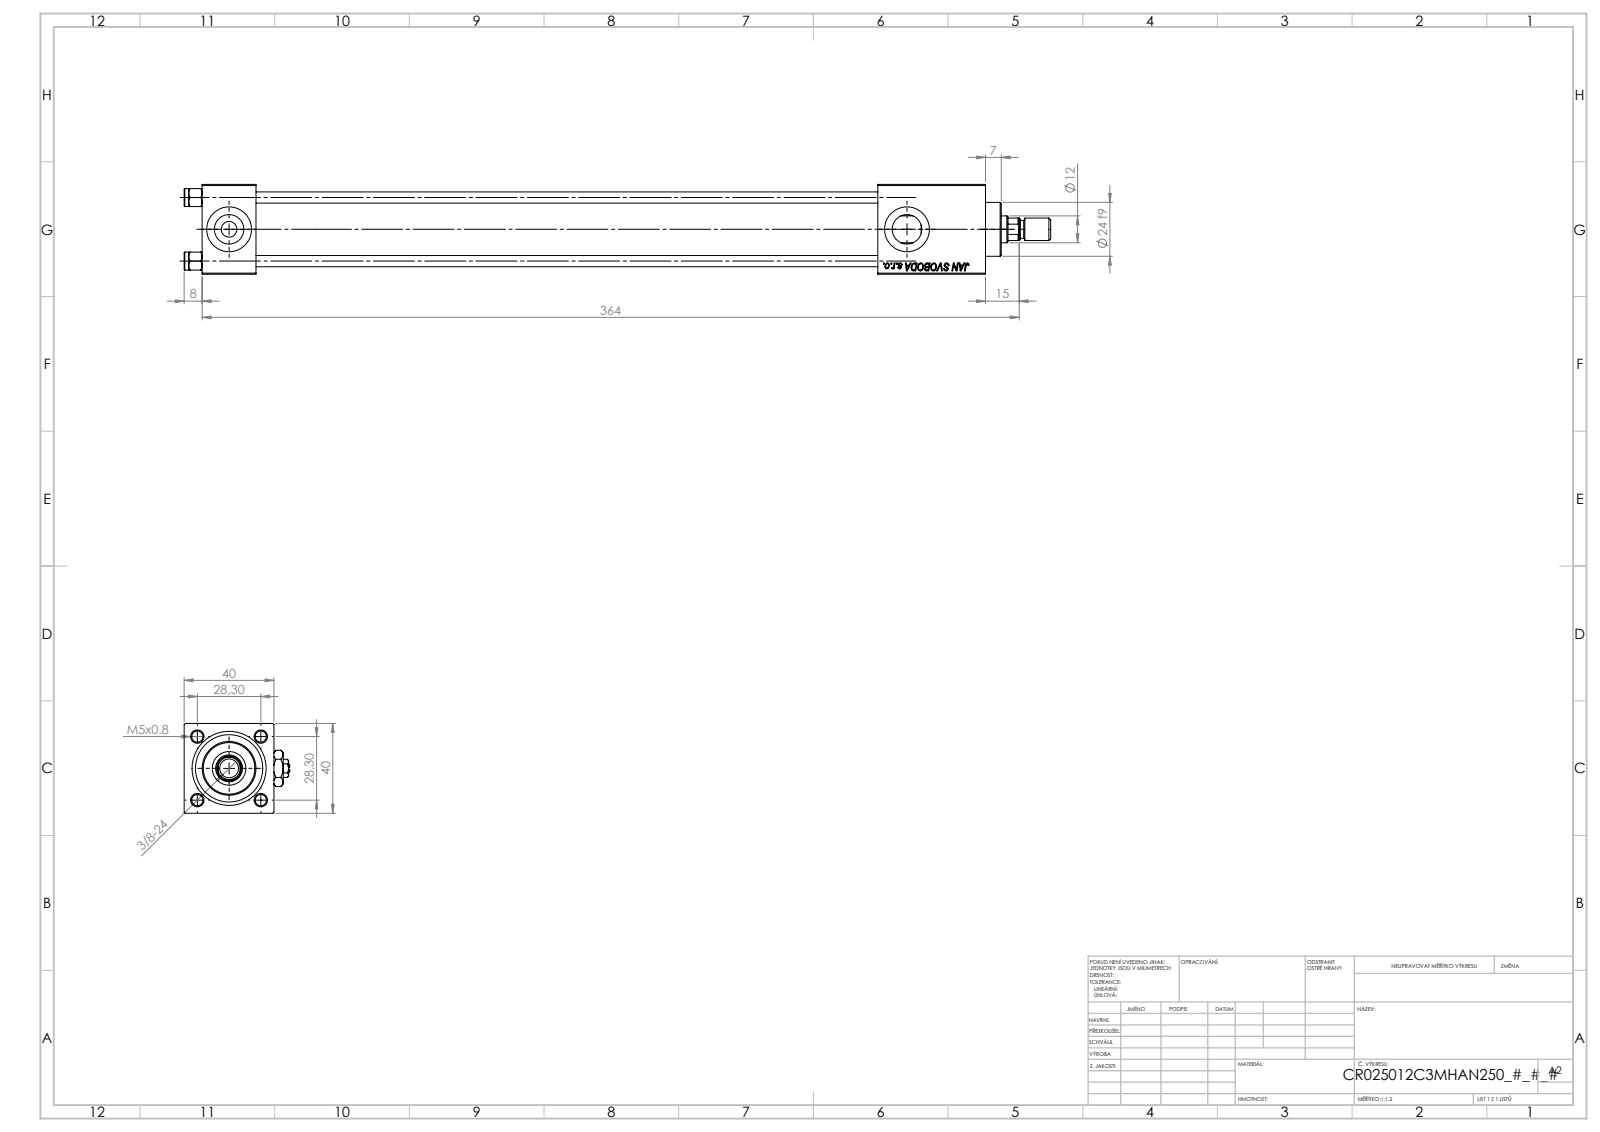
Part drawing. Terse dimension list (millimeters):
name: NUT_M5_C; ROD_END_AH; V215CR_C_TYCINKA; V215CR_C_Body (+3 more)
written by: SolidWorks 2019 (CONFIG_CONTROL_DESIGN)
unit: mm
bodies: 14 solids, 1262 faces (576 planar, 102 cylindrical, 584 other)
size: 386 × 47 × 40
volume: 246 789 mm³; area: 120 406 mm²
holes: 4× ⌀5, 3× ⌀20, 2× ⌀7, 2× ⌀13.16, 1× ⌀6.5, 1× ⌀12, 1× ⌀15, 1× ⌀25, 1× ⌀30
bosses: 5× ⌀8, 1× ⌀31, 1× ⌀24, 1× ⌀10
rounds: 1× R5.5
face distances: 40, 24, 39.8, 48, 320.3, 296.3, 301, 277, 19.3, 349
hole spacings: 20.01, 28.3, 40.02, 302
